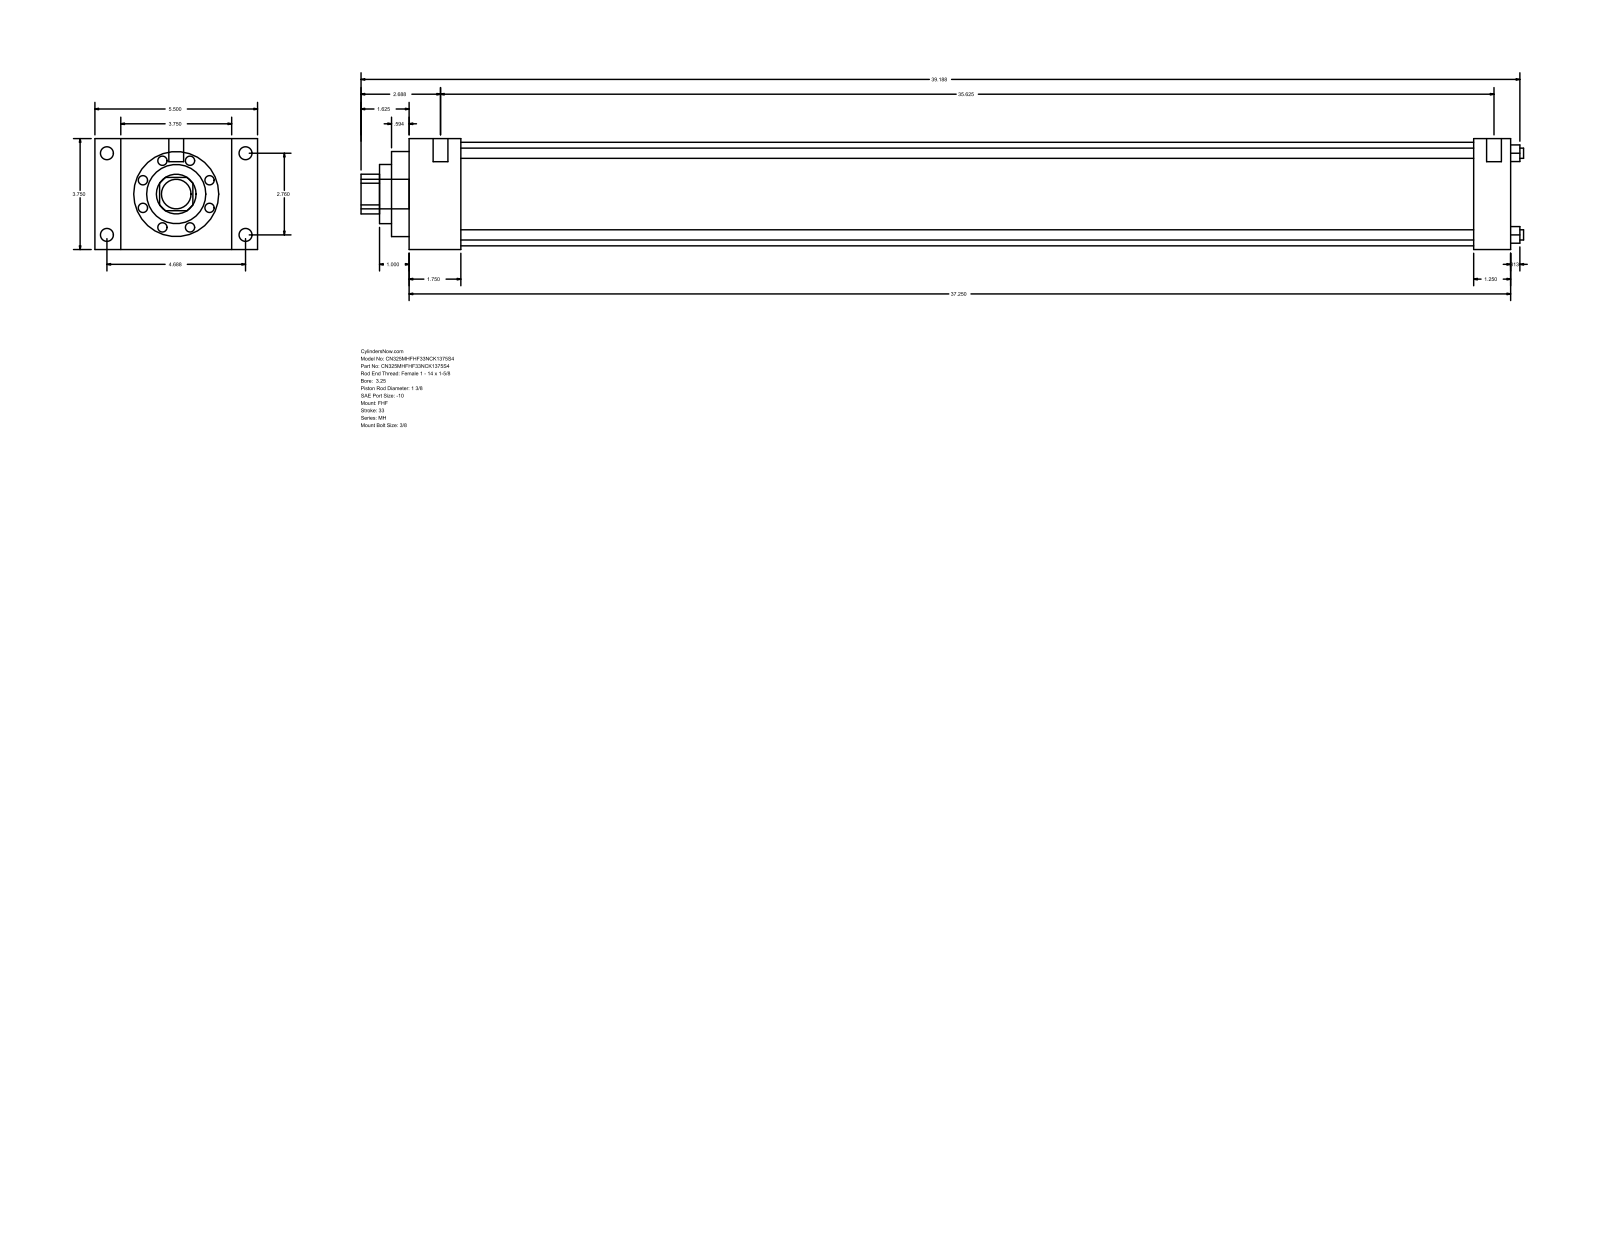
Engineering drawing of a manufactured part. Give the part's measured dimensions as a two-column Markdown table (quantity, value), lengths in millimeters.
| quantity | value |
| --- | --- |
| part name | MH_FHF__0325_1.375 |
| STEP written by | GSSL Pune (CONFIG_CONTROL_DESIGN) |
| units | millimeters |
| bodies | 0 solids, 90 faces (61 planar, 29 cylindrical, 0 other) |
| overall size | 998.54 × 139.7 × 95.25 |
| round holes (diameter × count) | 8.76 × 4, 34.92 × 1, 50.8 × 1, 73.03 × 1, 88.9 × 1 |
| round bosses / shafts (diameter × count) | 11.13 × 4, 5.56 × 4, 12.7 × 2, 25.4 × 1 |
| partial cylindrical surfaces (radius × count) | 17.06 × 1 |
| main face-to-face distances | 95.24, 946.15, 44.45, 901.7, 22.23, 117.47, 139.7, 914.4, 869.95, 31.75 |
| hole center spacings | 49.57, 70.1, 99.14 |
